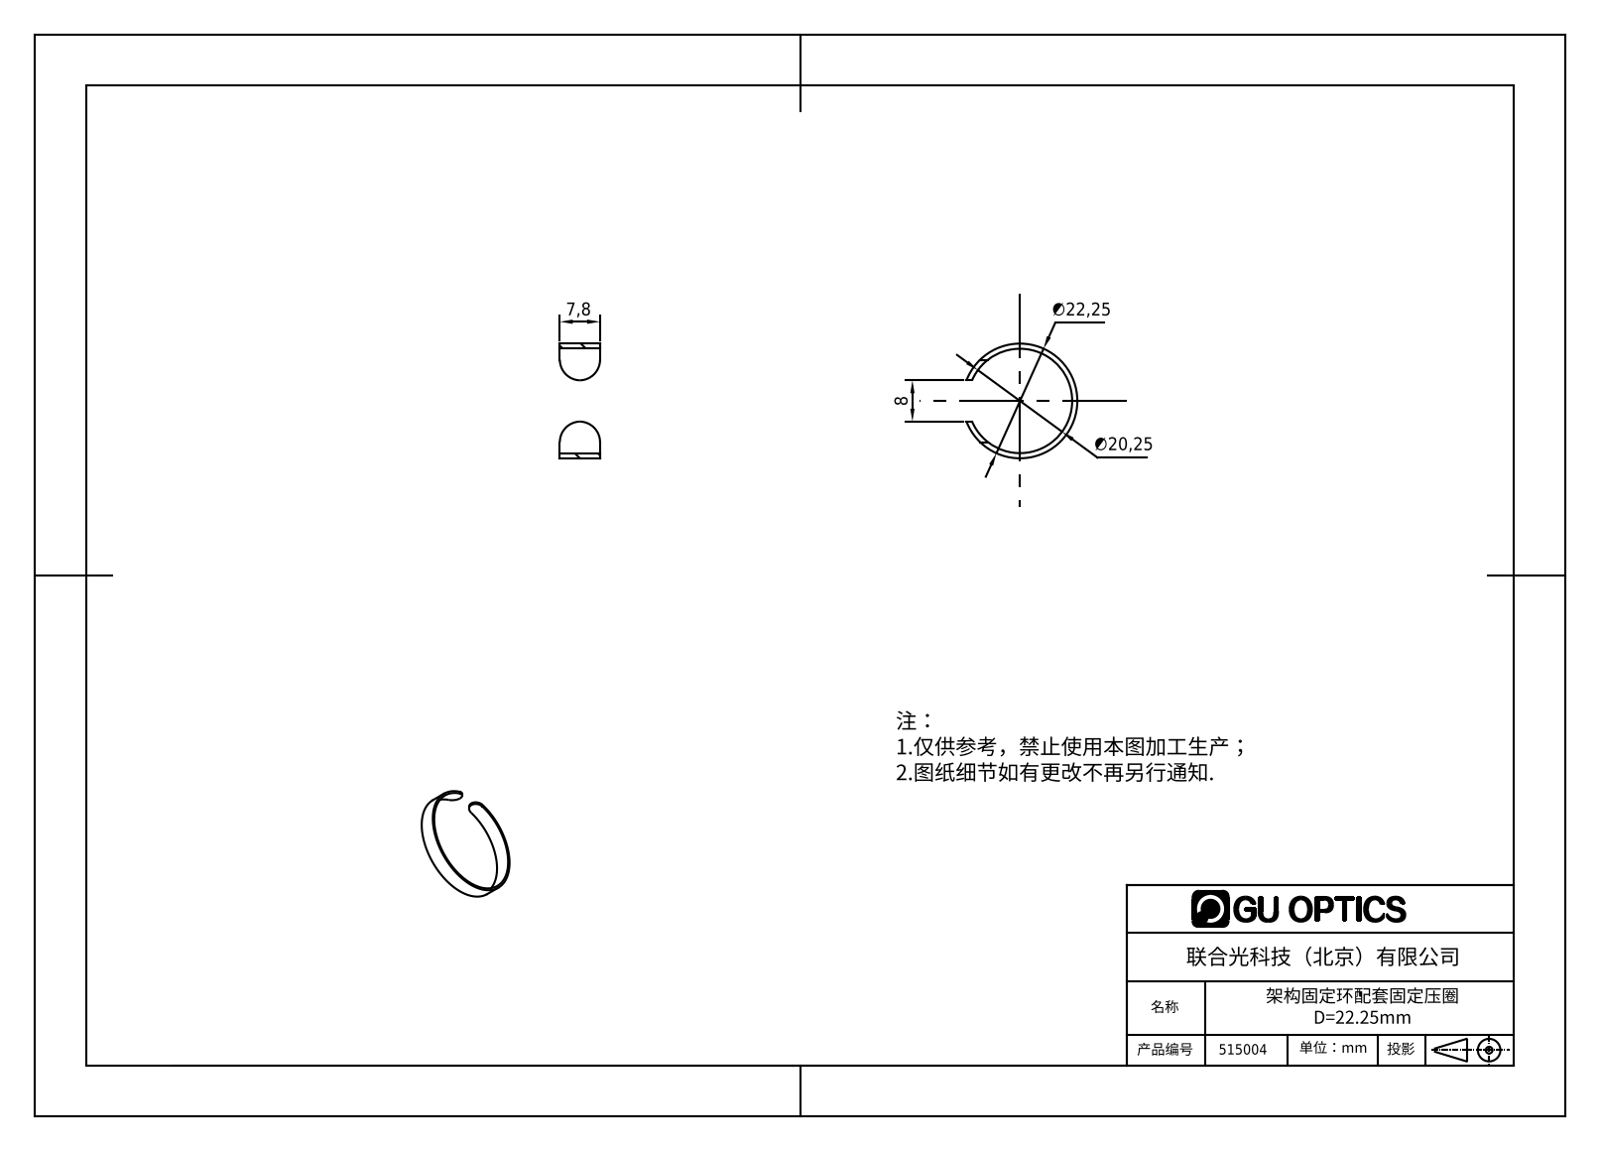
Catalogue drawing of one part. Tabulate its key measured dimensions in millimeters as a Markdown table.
| quantity | value |
| --- | --- |
| part name | 515004 |
| STEP written by | SolidWorks 2016 (CONFIG_CONTROL_DESIGN) |
| units | millimeters |
| bodies | 1 solid, 12 faces (2 planar, 10 cylindrical, 0 other) |
| overall size | 22.25 × 21.51 × 7.8 |
| volume | 441 mm³ |
| surface area | 1 009 mm² |
| round holes (diameter × count) | 20.25 × 1 |
| round bosses / shafts (diameter × count) | 22.25 × 1 |
| partial cylindrical surfaces (radius × count) | 4 × 4 |
| main face-to-face distances | 7.8 |
